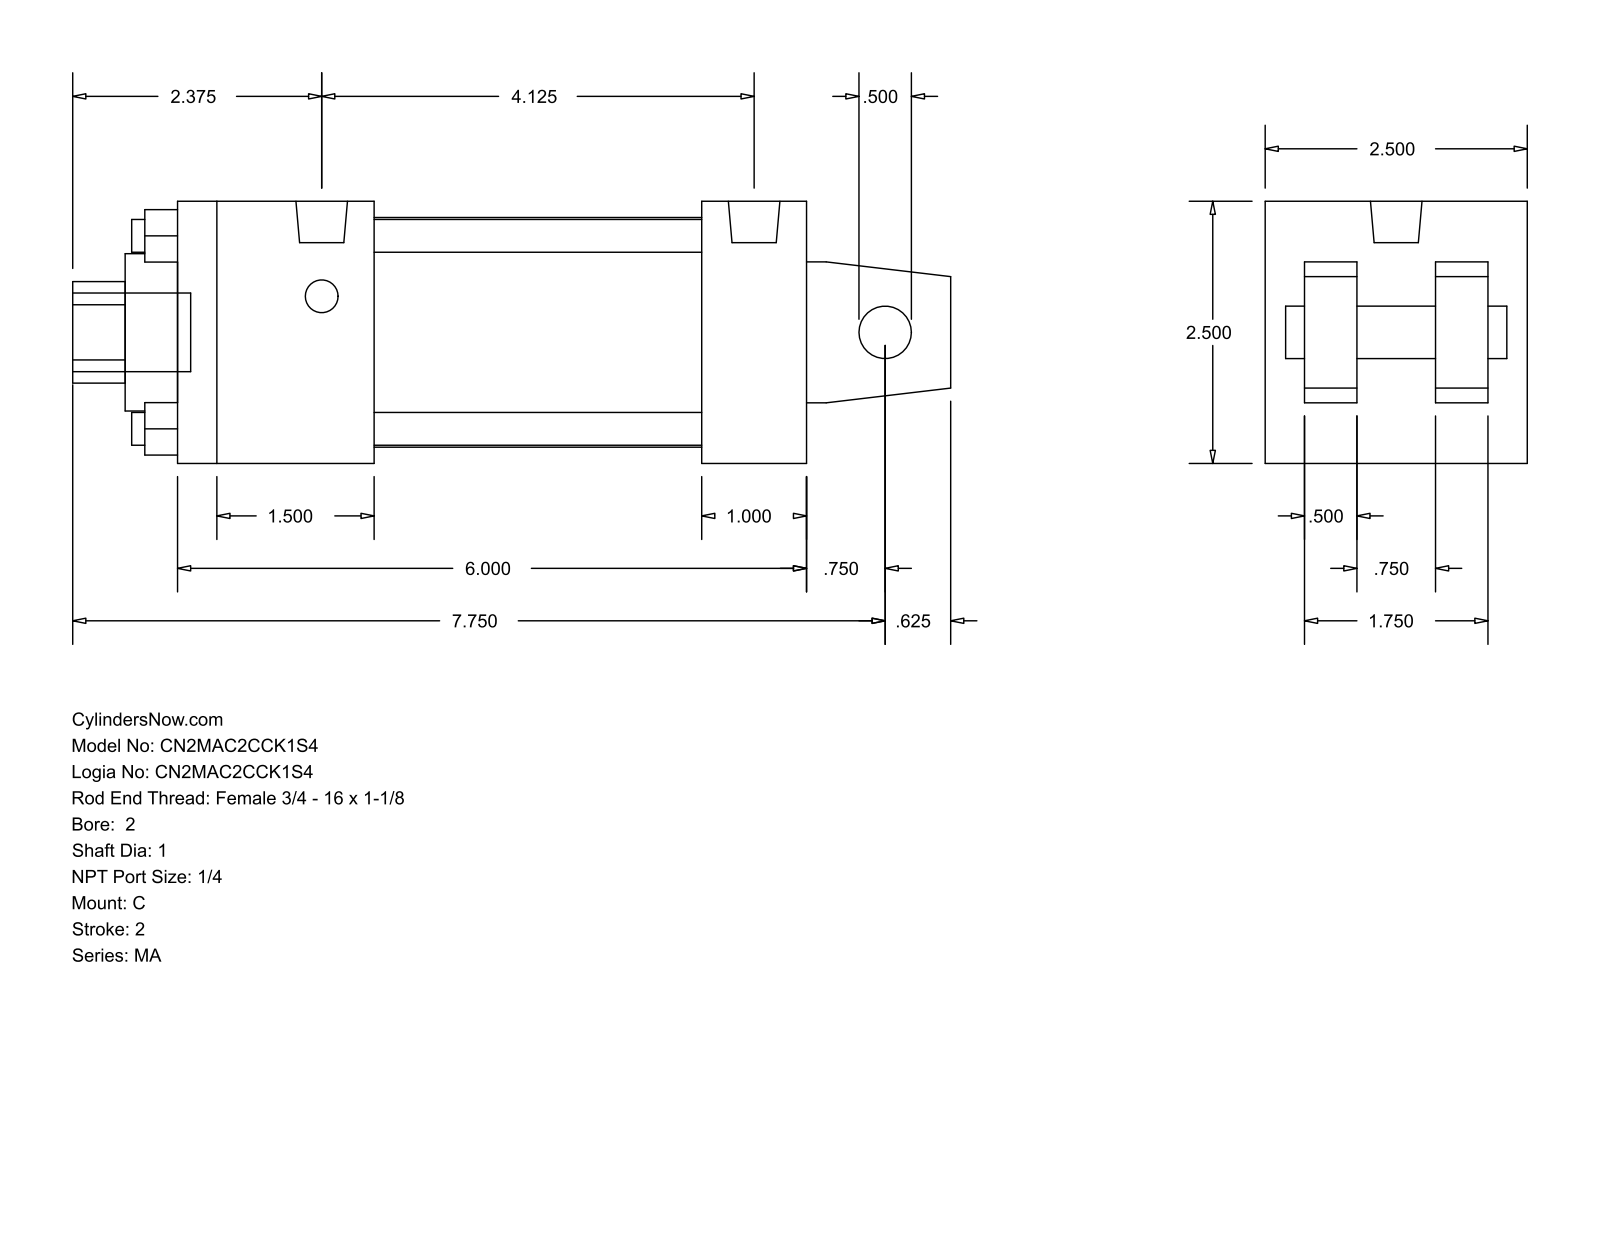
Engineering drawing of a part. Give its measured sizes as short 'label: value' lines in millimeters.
name: MA_C__0200_1
written by: GSSL Pune (CONFIG_CONTROL_DESIGN)
unit: mm
bodies: 0 solids, 103 faces (76 planar, 27 cylindrical, 0 other)
size: 212.72 × 63.5 × 63.5
holes: 4× ⌀7.94, 1× ⌀12.7, 1× ⌀25.4, 1× ⌀38.1, 1× ⌀55.63
bosses: 4× ⌀7.94, 2× ⌀12.49, 1× ⌀19.05
rounds: 1× R12.29
face distances: 63.5, 12.7, 152.4, 22.22, 41.28, 9.52, 53.98, 31.76, 47.63, 25.4
hole spacings: 33.05, 46.74, 66.1
